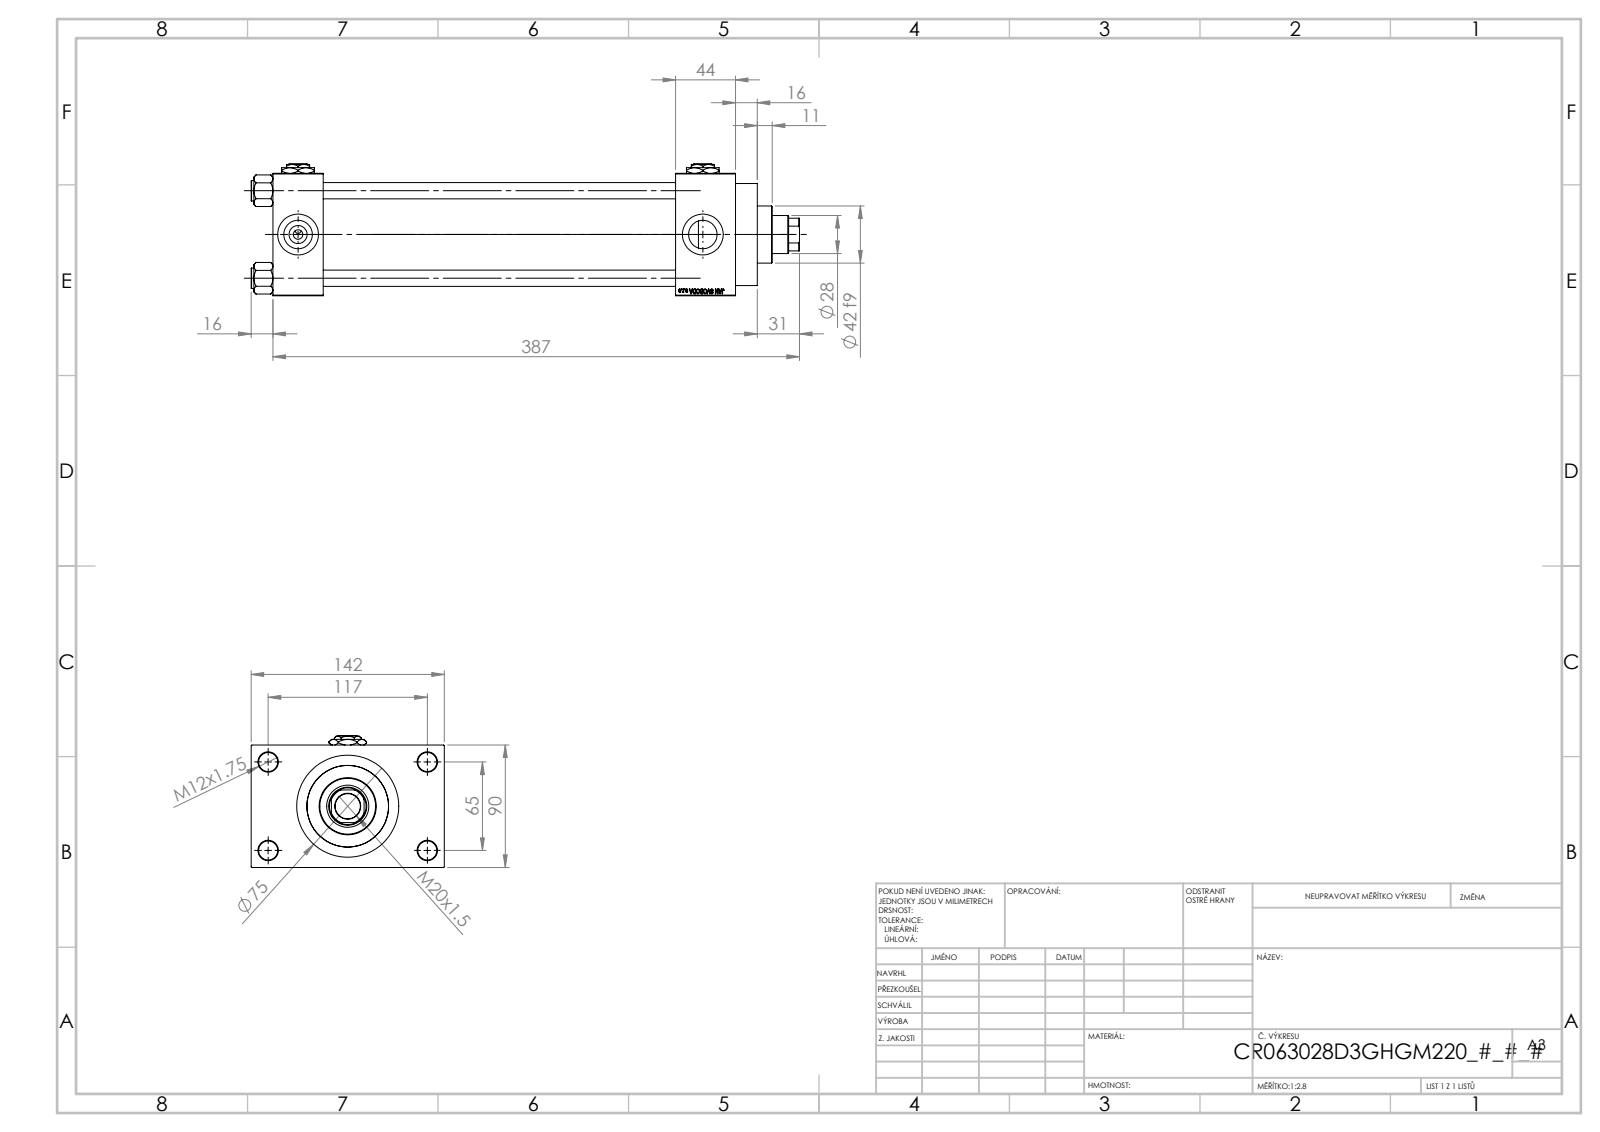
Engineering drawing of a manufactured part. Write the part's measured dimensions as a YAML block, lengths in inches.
part_name: "V215CR_D_TYCINKA; V215_VC_A; V215CR_D_Body; V215CR_VCP_D (+2 more)"
step_written_by: "SolidWorks 2019 (CONFIG_CONTROL_DESIGN)"
units: inches
bodies: {solids: 13, faces: 1204, planar: 545, cylindrical: 99, other: 560}
overall_size: [15.866, 5.591, 3.819]
volume: 87.2
surface_area: 520.2
round_holes:
  - {diameter: 0.472, count: 4}
  - {diameter: 0.551, count: 4}
  - {diameter: 0.825, count: 4}
  - {diameter: 1.181, count: 4}
  - {diameter: 0.276, count: 3}
  - {diameter: 0.728, count: 1}
  - {diameter: 1.102, count: 1}
  - {diameter: 1.22, count: 1}
  - {diameter: 1.969, count: 1}
  - {diameter: 2.362, count: 1}
  - {diameter: 2.48, count: 1}
round_bosses_or_shafts:
  - {diameter: 0.591, count: 4}
  - {diameter: 2.953, count: 1}
  - {diameter: 2.717, count: 1}
  - {diameter: 1.654, count: 1}
partial_cylinders:
  - {radius: 0.531, count: 1}
face_to_face_distances: [3.543, 10.197, 1.457, 11.654, 11.929, 13.386, 1.732, 1.024, 4.567, 0.63]
hole_center_spacings: [1.037, 1.79, 2.531, 2.635, 2.748, 3.569, 4.383, 2.559]
